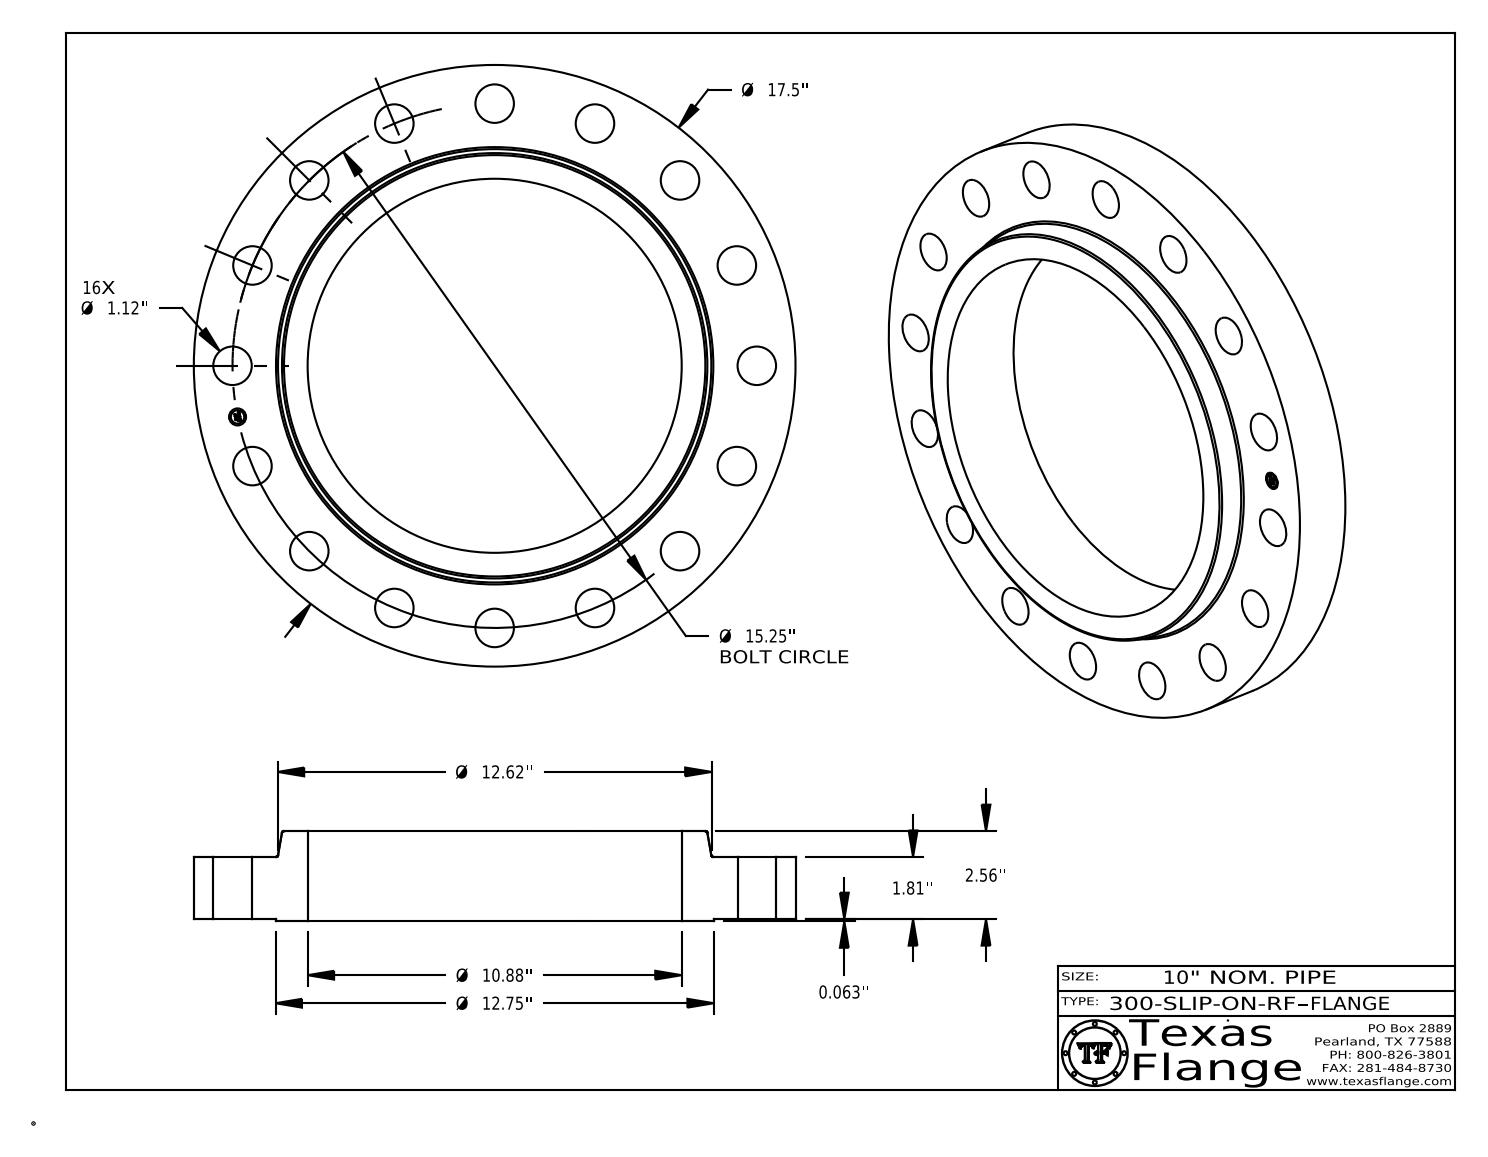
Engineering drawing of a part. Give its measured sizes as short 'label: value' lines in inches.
name: 300-SLIP-ON-RF
written by: CATIA V5 STEP AP214 (AUTOMOTIVE_DESIGN)
unit: in
bodies: 1 solid, 433 faces (369 planar, 58 cylindrical, 6 other)
size: 17.5 × 17.5 × 2.623
volume: 262.8 in³; area: 580.6 in²
holes: 16× ⌀1.12, 1× ⌀0.495, 1× ⌀10.88
bosses: 8× ⌀0.03, 1× ⌀17.5, 1× ⌀12.75, 1× ⌀0.39
face distances: 1.81, 0.063, 1.872, 2.622, 2.56, 0.75, 0.015, 1.857, 1.795, 0.765
hole spacings: 8.472, 10.783, 14.957, 14.089, 7.625, 2.975, 2.975, 5.836
